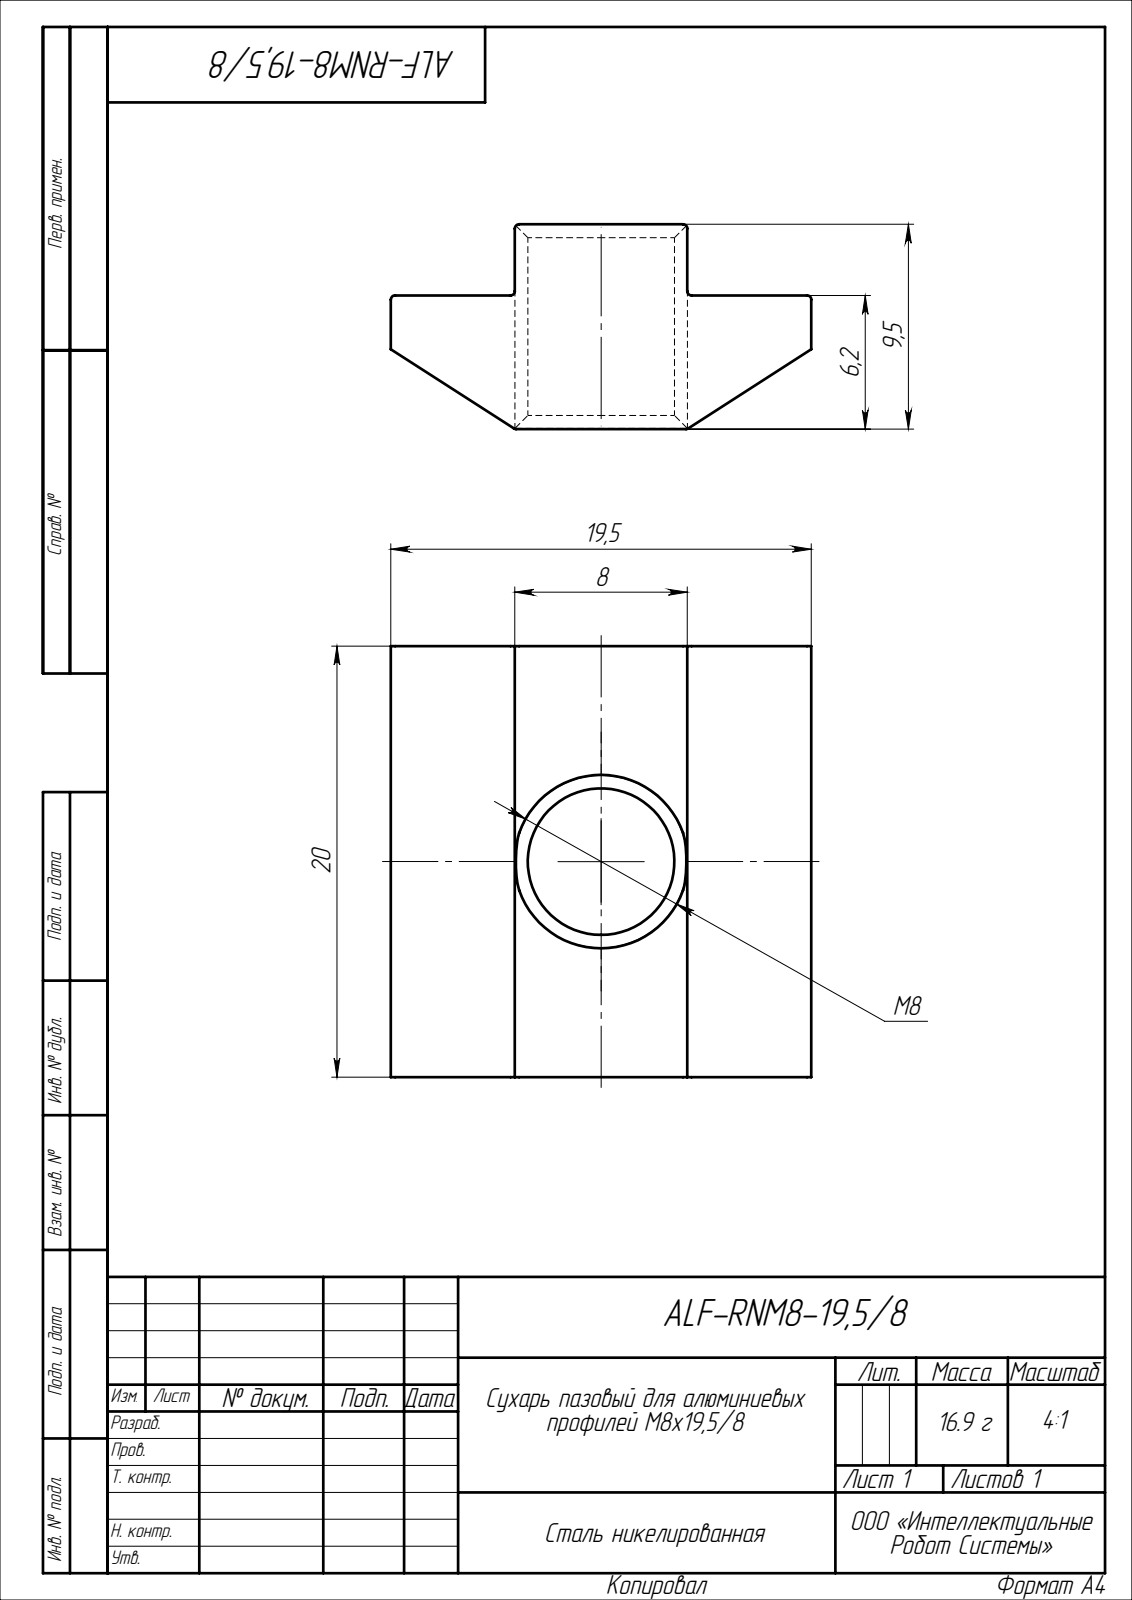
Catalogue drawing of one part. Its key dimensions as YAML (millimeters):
part_name: "ALF-RNM8-19,5_8"
step_written_by: "SolidWorks 2022 (CONFIG_CONTROL_DESIGN)"
units: millimeters
bodies: {solids: 1, faces: 28, planar: 14, cylindrical: 10, other: 4}
overall_size: [20, 19.5, 9.5]
volume: 2166
surface_area: 1413
round_holes:
  - {diameter: 6.8, count: 1}
partial_cylinders:
  - {radius: 0.2, count: 8}
face_to_face_distances: [20, 6.2, 9.5, 3.3, 5.75, 13.75, 8, 19.5]
